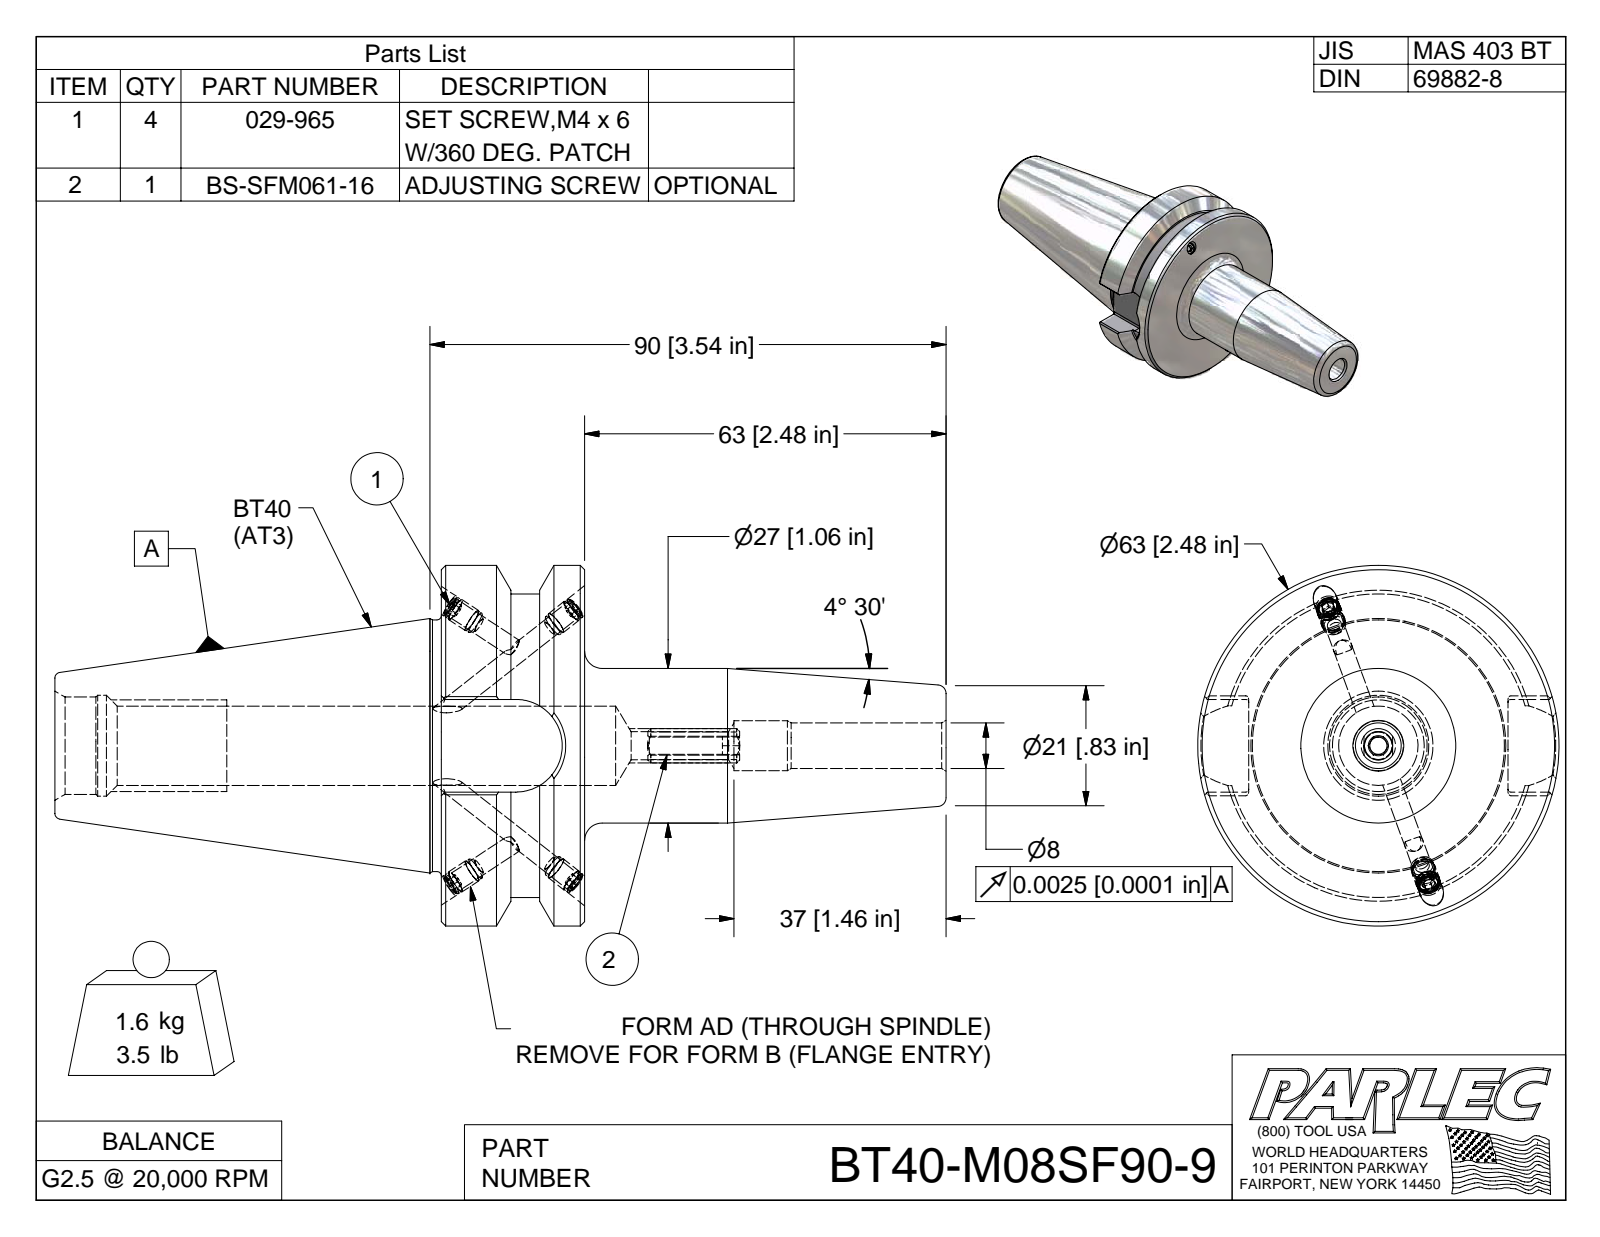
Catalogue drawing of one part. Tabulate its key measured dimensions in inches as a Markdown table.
| quantity | value |
| --- | --- |
| part name | BT40-M08SF90-9; BT40BC-M08SF90-9-1; 029-965; BS-SFM061-16 |
| STEP written by | Autodesk Inventor 2009 (AUTOMOTIVE_DESIGN) |
| units | inches |
| bodies | 6 solids, 178 faces (79 planar, 43 cylindrical, 56 other) |
| overall size | 6.118 × 2.48 × 2.48 |
| volume | 9.002 in³ |
| surface area | 47.22 in² |
| round holes (diameter × count) | 0.13 × 4, 0.161 × 4, 0.314 × 1, 0.344 × 1, 0.694 × 1 |
| round bosses / shafts (diameter × count) | 0.165 × 4, 0.157 × 4, 2.48 × 1, 2.087 × 1, 1.75 × 1, 1.73 × 1, 1.063 × 1 |
| partial cylindrical surfaces (radius × count) | 0.02 × 8, 0.118 × 1, 0.319 × 1 |
| main face-to-face distances | 0.984, 1.78, 3.465, 2.481, 2.653, 3.637, 6.119, 0.637, 0.197, 0.792 |
